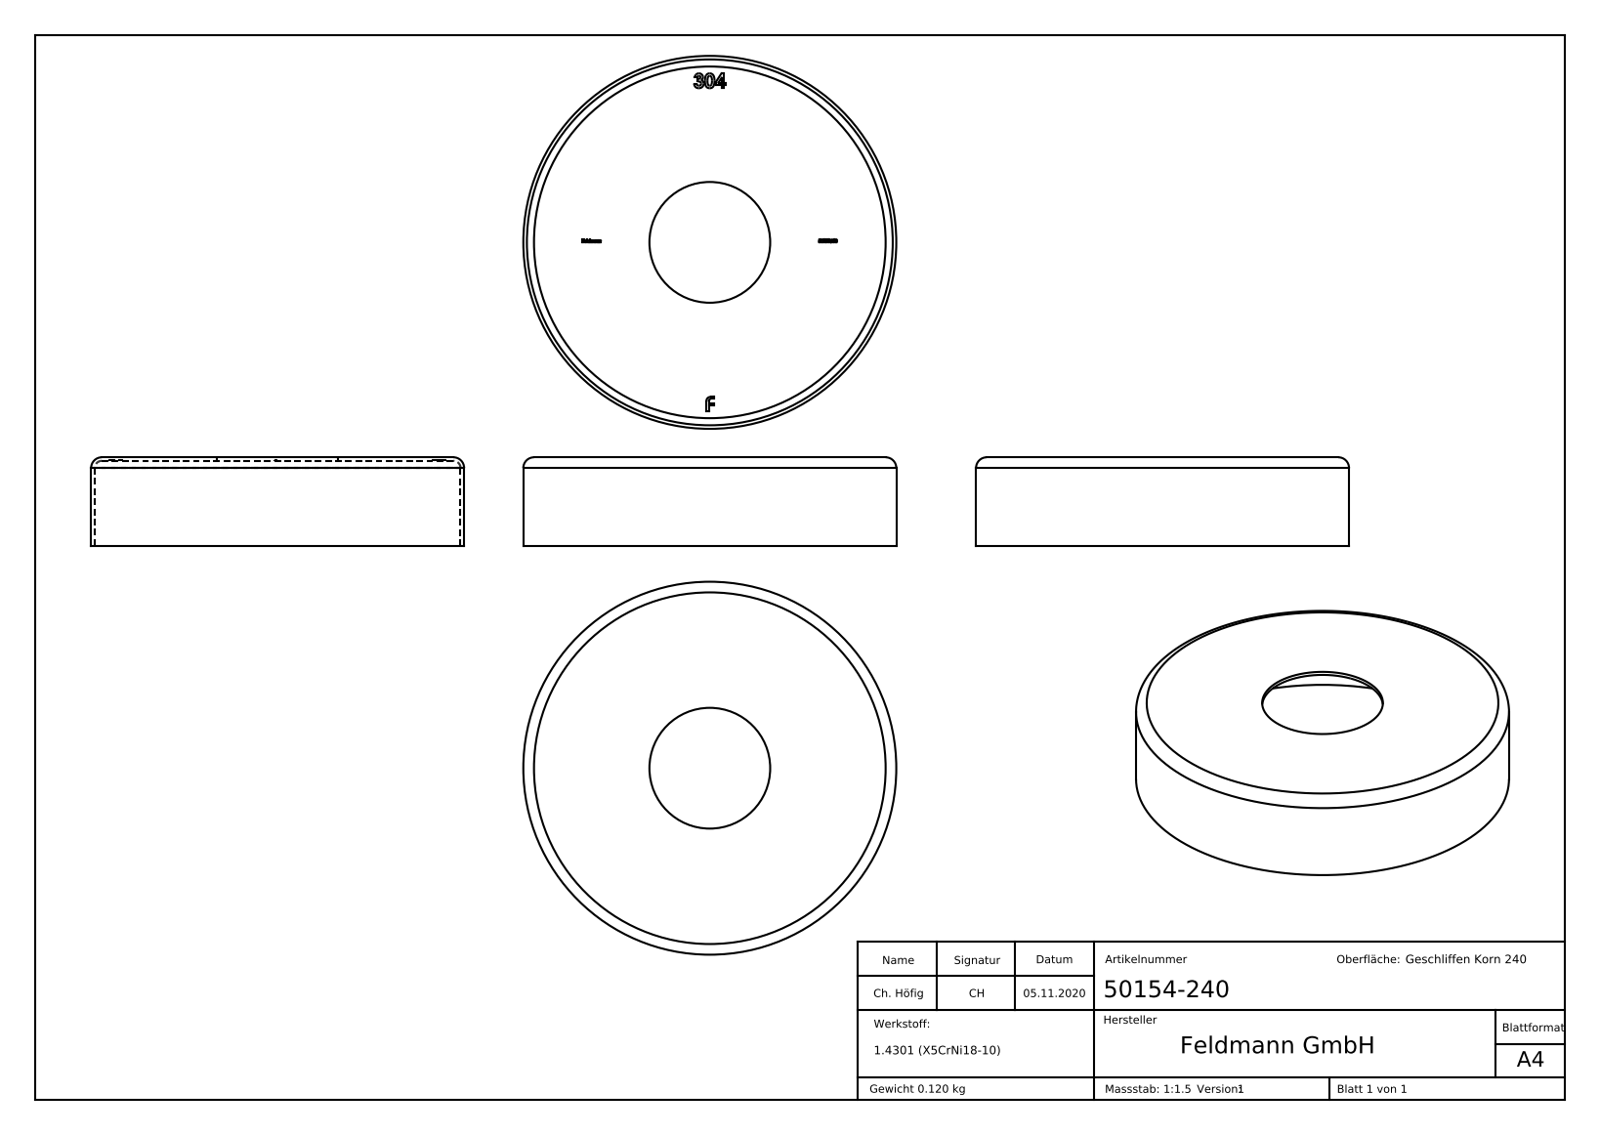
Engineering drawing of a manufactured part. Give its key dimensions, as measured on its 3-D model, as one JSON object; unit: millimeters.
{"part_name": "50154-240", "step_written_by": "SolidWorks 2018 (CONFIG_CONTROL_DESIGN)", "units": "millimeters", "bodies": {"solids": 1, "faces": 291, "planar": 168, "cylindrical": 6, "other": 117}, "overall_size": [105, 105, 25], "volume_mm3": 15236, "surface_area_mm2": 30926, "round_holes": [[34, 1], [103, 1]], "round_bosses_or_shafts": [[105, 1]], "face_to_face_distances": [1, 24, 25, 24.1, 0.9, 0.71, 5, 4.29, 32.41, 0.58]}
